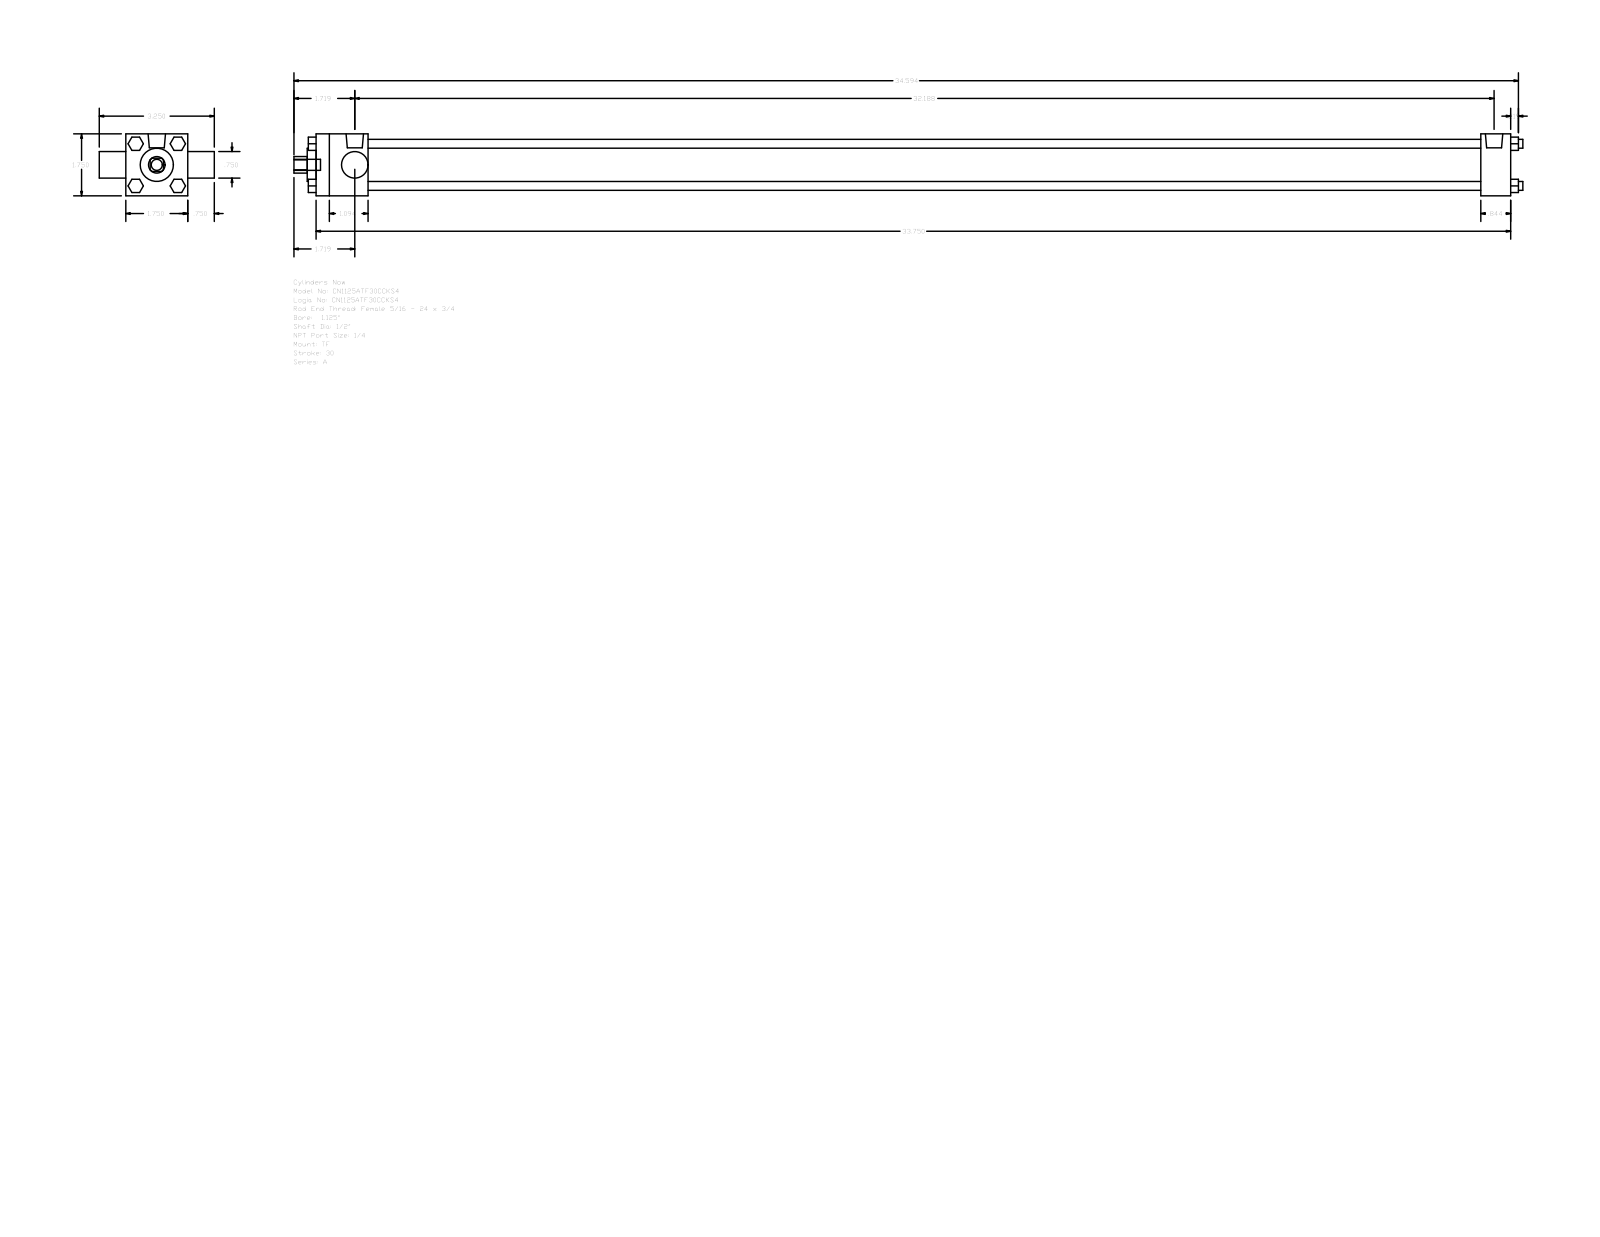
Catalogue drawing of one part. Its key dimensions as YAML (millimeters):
part_name: "A_TF__0112_0.5"
step_written_by: "GSSL Pune (CONFIG_CONTROL_DESIGN)"
units: millimeters
bodies: {solids: 0, faces: 120, planar: 92, cylindrical: 28, other: 0}
overall_size: [881.86, 82.55, 44.45]
round_holes:
  - {diameter: 12.7, count: 1}
  - {diameter: 19.05, count: 1}
  - {diameter: 23.81, count: 1}
  - {diameter: 31.88, count: 1}
round_bosses_or_shafts:
  - {diameter: 6.35, count: 4}
  - {diameter: 5.56, count: 3}
  - {diameter: 12.49, count: 2}
  - {diameter: 7.94, count: 1}
partial_cylinders:
  - {radius: 5.94, count: 1}
face_to_face_distances: [44.46, 857.24, 835.81, 21.43, 37.3, 798.51, 819.94, 19.04, 63.5, 9.53]
